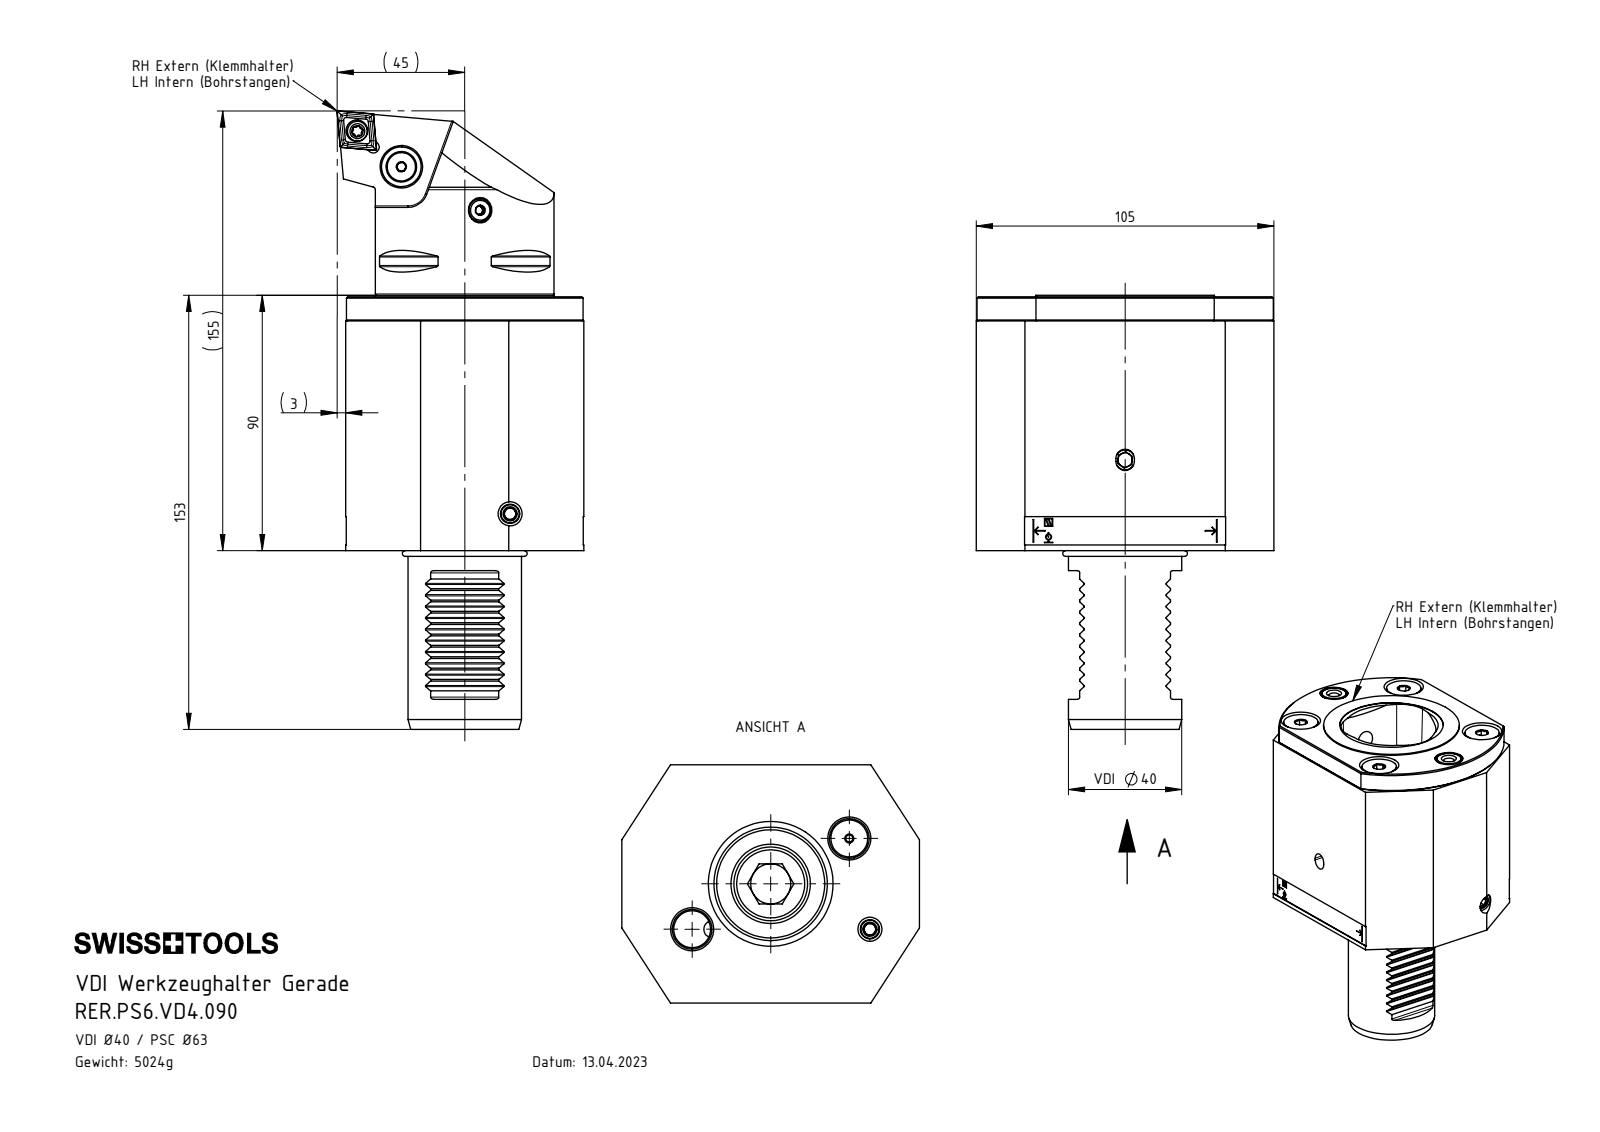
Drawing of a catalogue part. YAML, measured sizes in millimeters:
part_name: "VD4-ER1.040.066; DIN 3771 - 58x2.5; ISO 4026 - M8 x 8; DIN 6325_ø5x12_2x6 (+8 more)"
step_written_by: "SolidWorks 2022 (AUTOMOTIVE_DESIGN)"
units: millimeters
bodies: {solids: 27, faces: 997, planar: 385, cylindrical: 265, other: 347}
overall_size: [153, 105, 84]
volume: 664720
surface_area: 147650
round_holes:
  - {diameter: 6.8, count: 8}
  - {diameter: 5, count: 6}
  - {diameter: 9, count: 5}
  - {diameter: 4, count: 4}
  - {diameter: 13, count: 4}
  - {diameter: 4.2, count: 2}
  - {diameter: 5.5, count: 2}
  - {diameter: 8.5, count: 2}
  - {diameter: 12, count: 2}
  - {diameter: 14, count: 2}
  - {diameter: 2.4, count: 1}
  - {diameter: 2.5, count: 1}
round_bosses_or_shafts:
  - {diameter: 8, count: 7}
  - {diameter: 16, count: 5}
  - {diameter: 8.5, count: 2}
  - {diameter: 5, count: 2}
  - {diameter: 63, count: 1}
  - {diameter: 62.7, count: 1}
  - {diameter: 59, count: 1}
  - {diameter: 58.8, count: 1}
partial_cylinders:
  - {radius: 0.3, count: 20}
  - {radius: 0.1, count: 6}
  - {radius: 0.8, count: 4}
  - {radius: 4.5, count: 4}
  - {radius: 3.25, count: 2}
  - {radius: 5, count: 2}
  - {radius: 11, count: 1}
  - {radius: 19, count: 1}
face_to_face_distances: [81, 105.05, 84, 24, 57, 8.5, 89.5, 65.5, 3, 105]
hole_center_spacings: [32.13, 33.11, 42.43, 47.73, 57.03, 60, 79.85, 14.19]
